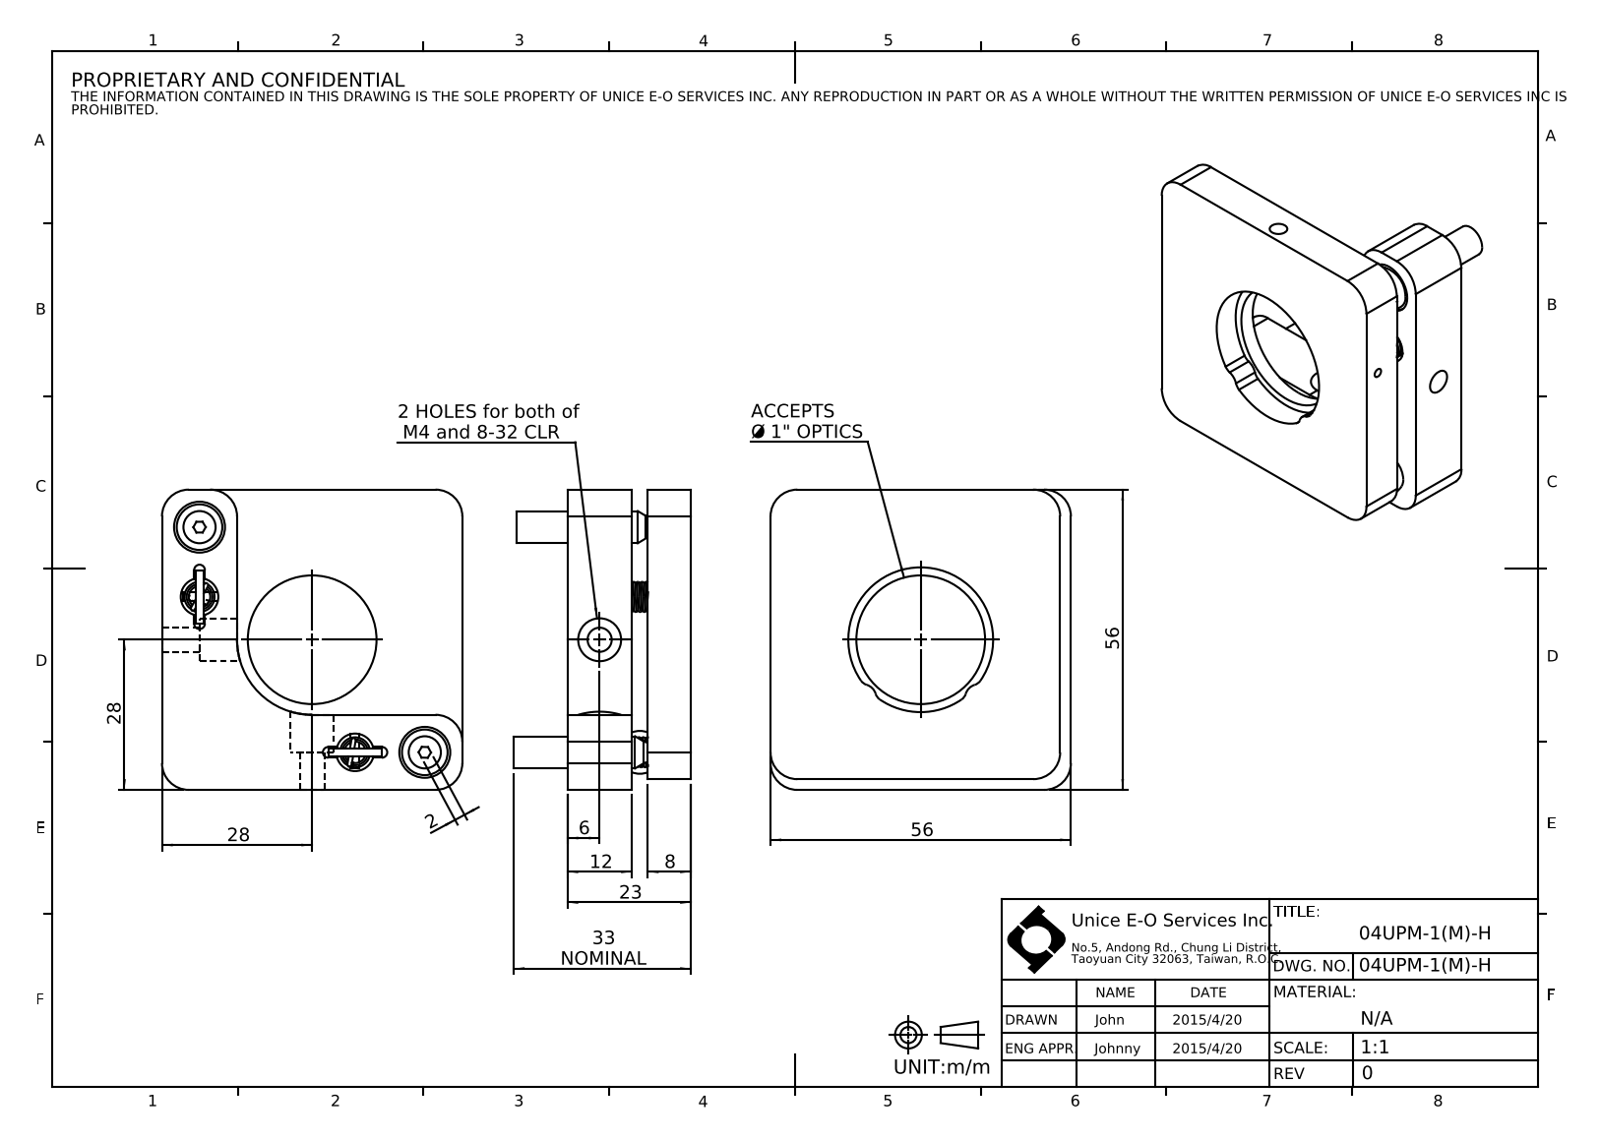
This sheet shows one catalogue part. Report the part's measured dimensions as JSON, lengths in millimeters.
{"part_name": "04UPM-1(M)-H", "step_written_by": "SolidWorks 2021 (CONFIG_CONTROL_DESIGN)", "units": "millimeters", "bodies": {"solids": 19, "faces": 277, "planar": 105, "cylindrical": 116, "other": 56}, "overall_size": [56, 56, 33], "volume_mm3": 34034, "surface_area_mm2": 18603, "round_holes": [[1.2, 4], [1.7, 2], [4, 2], [4.5, 2], [5.75, 2], [7, 2], [8, 2], [9.5, 2], [3.3, 1], [6.35, 1], [24, 1], [27, 1]], "round_bosses_or_shafts": [[0.8, 12], [1.6, 4], [9.45, 2], [6, 2], [6.3, 1], [4, 1], [2.5, 1]], "partial_cylinders_radius": [[5, 9], [1, 4], [2, 4], [2.5, 2], [14, 1]], "face_to_face_distances": [8, 12, 3, 23, 15, 11, 56, 2, 54, 42], "hole_center_spacings": [13, 16.12, 21.44, 22.47, 29.7, 34.29, 51.04, 8]}
